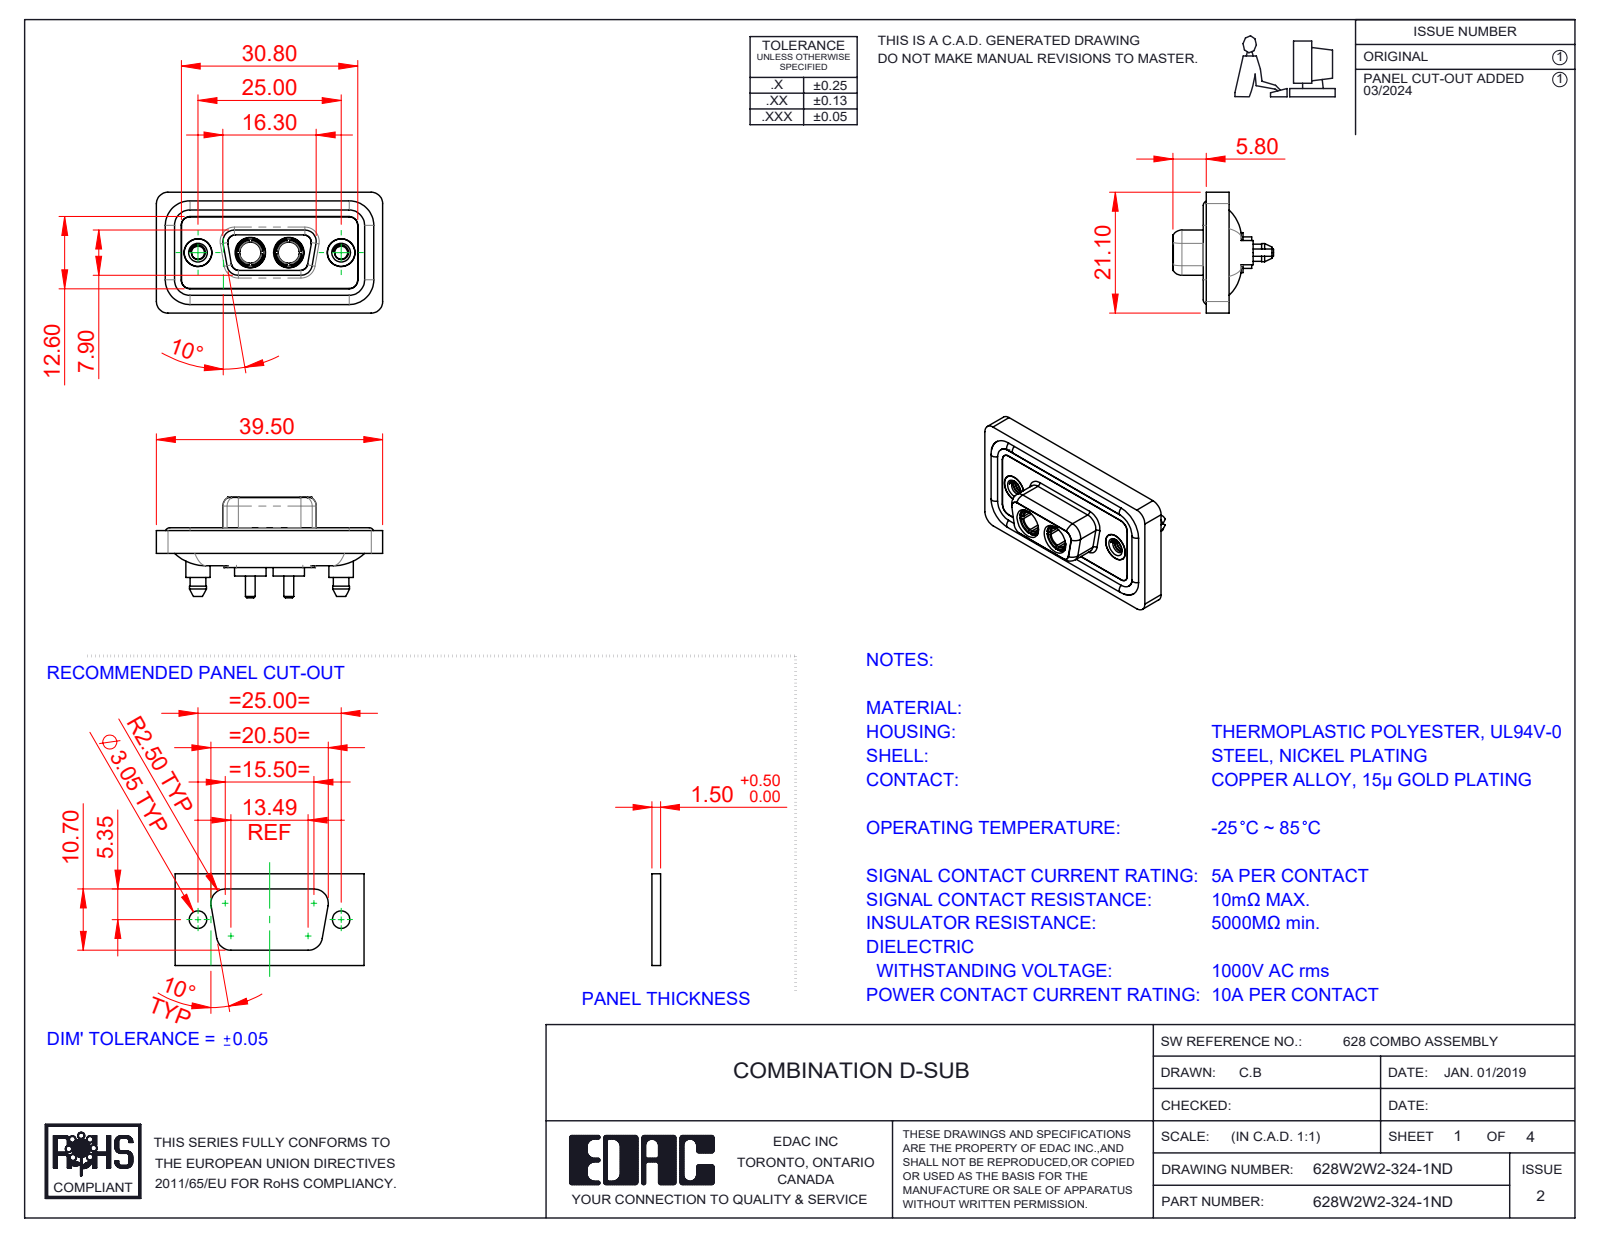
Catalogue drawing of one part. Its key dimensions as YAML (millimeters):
part_name: "628Combo Threaded Boardlock_D; 628Combo Shell Rear_09 Contacts; 628Combo Waterproof Housing_09 Contacts; 628Combo Shell Front_09 Contacts (+3 more)"
step_written_by: "SolidWorks 2023 (CONFIG_CONTROL_DESIGN)"
units: millimeters
bodies: {solids: 11, faces: 600, planar: 179, cylindrical: 282, other: 139}
overall_size: [39.5, 21.1, 17.55]
volume: 4819
surface_area: 7950
round_holes:
  - {diameter: 4.85, count: 4}
  - {diameter: 2.26, count: 2}
  - {diameter: 3.7, count: 2}
  - {diameter: 4, count: 2}
  - {diameter: 4.05, count: 2}
  - {diameter: 5, count: 2}
  - {diameter: 5.3, count: 2}
round_bosses_or_shafts:
  - {diameter: 1.6, count: 4}
  - {diameter: 5.5, count: 2}
  - {diameter: 5.4, count: 2}
  - {diameter: 5.2, count: 2}
  - {diameter: 4.96, count: 2}
  - {diameter: 4.95, count: 2}
  - {diameter: 4.8, count: 2}
  - {diameter: 4.75, count: 2}
partial_cylinders:
  - {radius: 1.5, count: 24}
  - {radius: 2, count: 18}
  - {radius: 1.6, count: 10}
  - {radius: 1.35, count: 8}
  - {radius: 0.25, count: 4}
  - {radius: 0.5, count: 4}
  - {radius: 0.6, count: 4}
  - {radius: 0.65, count: 4}
face_to_face_distances: [0.4, 1.8, 1.1, 2.9, 1.6, 0.5, 5.65, 1.5, 7.45, 4]
hole_center_spacings: [9.14, 15.86, 6.72, 25]
